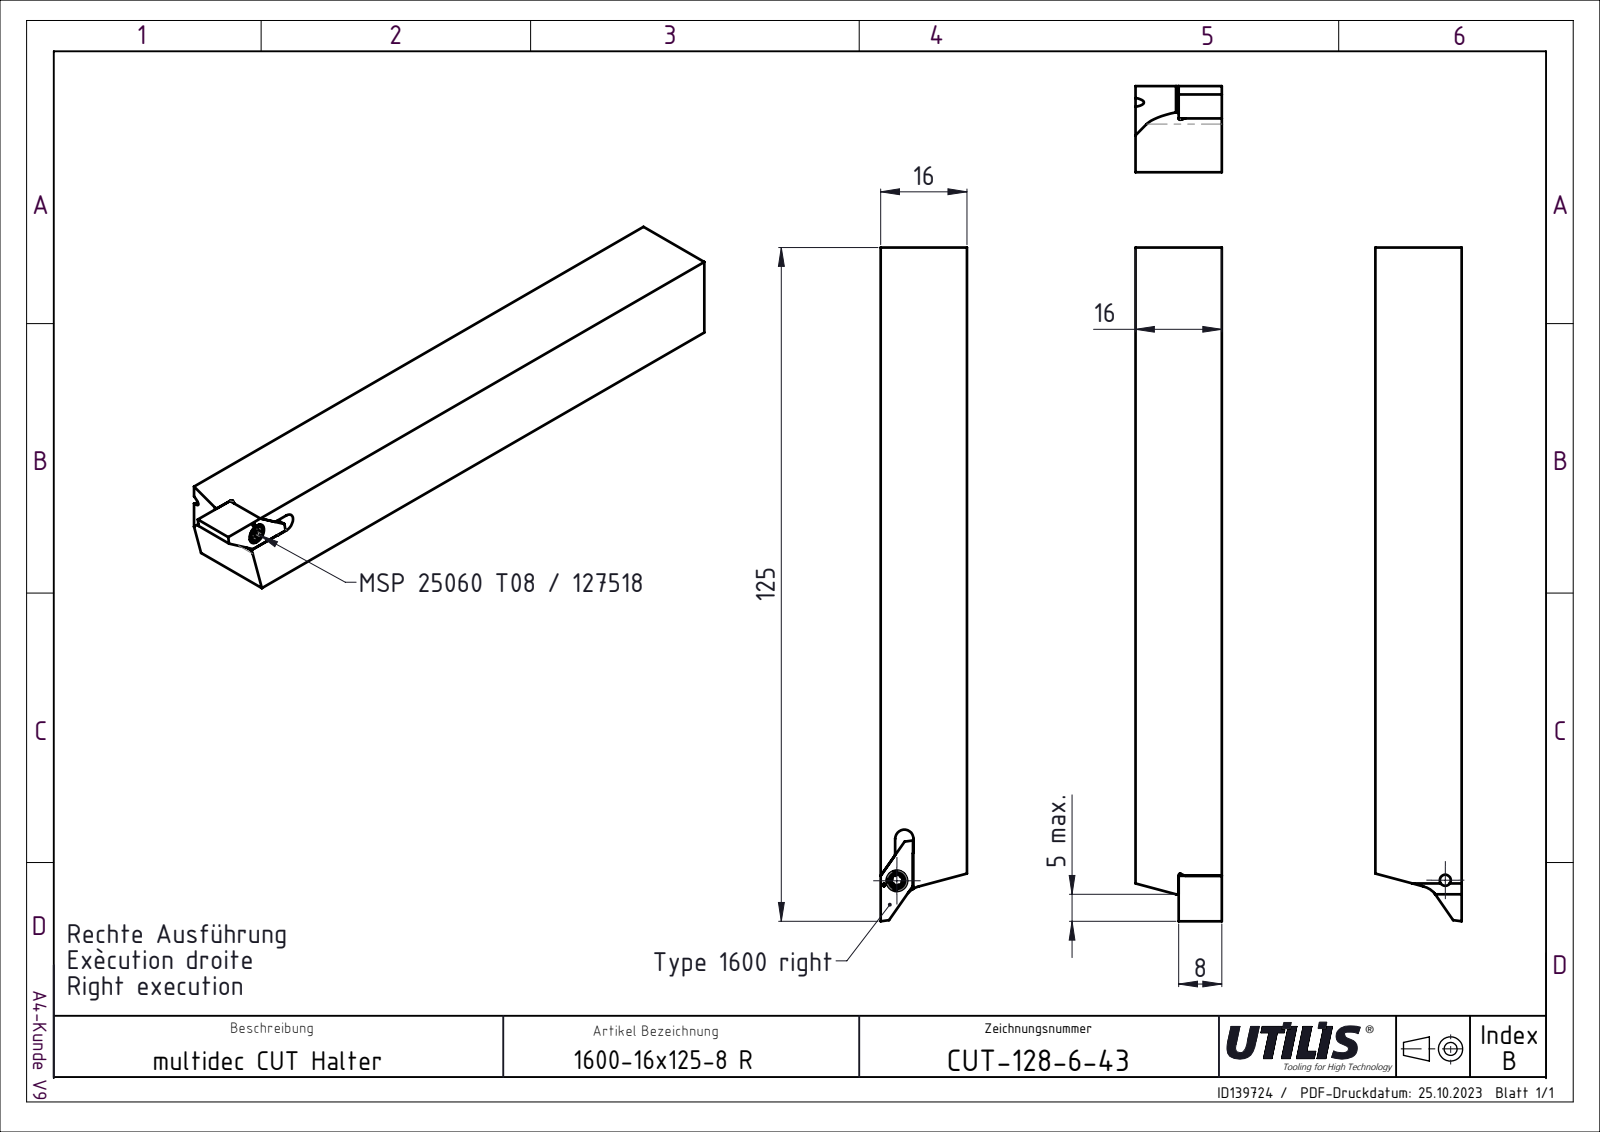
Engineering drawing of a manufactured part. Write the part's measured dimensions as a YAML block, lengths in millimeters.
part_name: "CUT-128-6_WSP_10011; CUT-128-6_43; CUT-128-6-43"
step_written_by: "SolidWorks 2023 (AUTOMOTIVE_DESIGN)"
units: millimeters
bodies: {solids: 2, faces: 46, planar: 36, cylindrical: 8, other: 2}
overall_size: [125, 16, 16]
volume: 30181
surface_area: 8661
round_holes:
  - {diameter: 2.05, count: 1}
  - {diameter: 3.1, count: 1}
  - {diameter: 3.8, count: 1}
partial_cylinders:
  - {radius: 0.5, count: 1}
  - {radius: 1.5, count: 1}
  - {radius: 1.55, count: 1}
  - {radius: 1.7, count: 1}
  - {radius: 4.1, count: 1}
face_to_face_distances: [16, 8, 6, 10, 13.3, 3.3, 2.7, 9.9, 3.4, 6.1]
